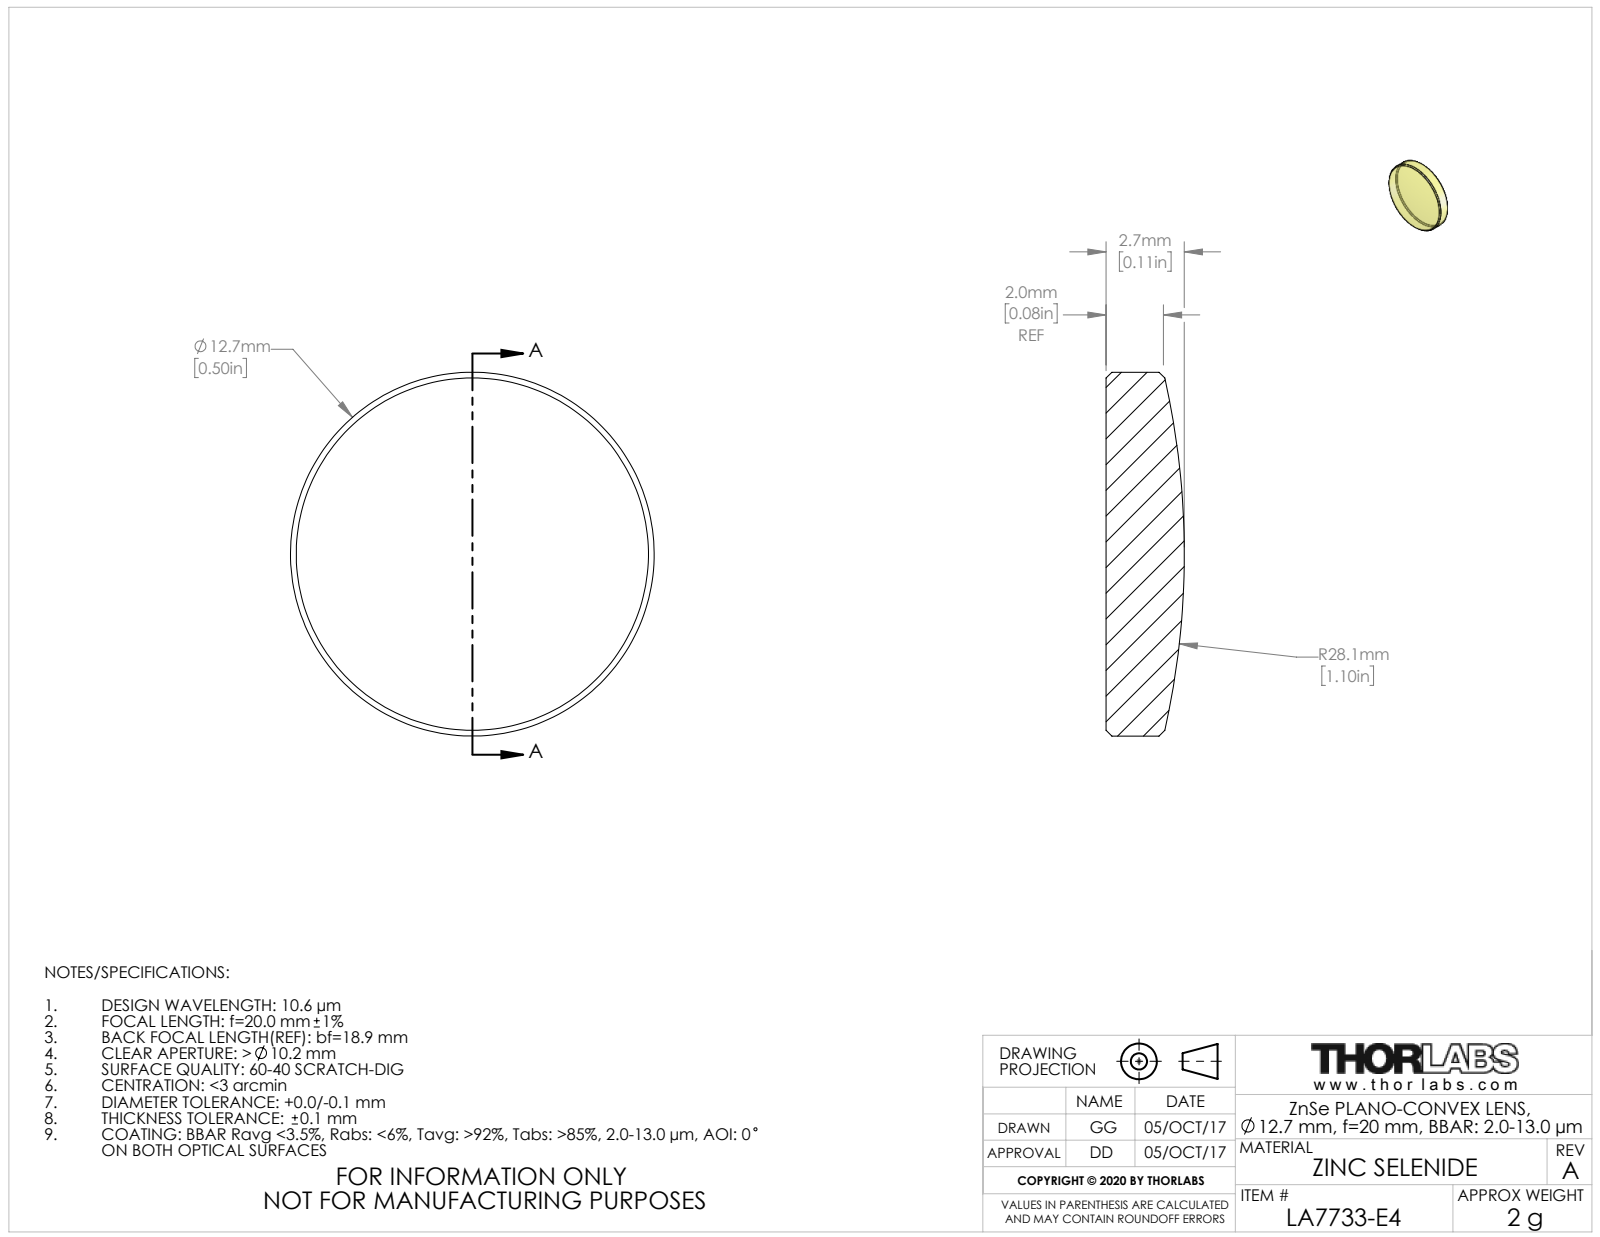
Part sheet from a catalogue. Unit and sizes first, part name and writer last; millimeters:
Units: millimetres
Overall size (bounding box): 12.7 × 12.7 × 2.73
Round bosses / shafts (diameter × count): ⌀12.7 ×1
Volume: 299 mm³ · Surface area: 327 mm²
Bodies: 1 solid, 9 faces (1 planar, 2 cylindrical, 6 other)
Part name (STEP PRODUCT): TTN098080-E0W
STEP written by: SolidWorks 2018 (CONFIG_CONTROL_DESIGN)
